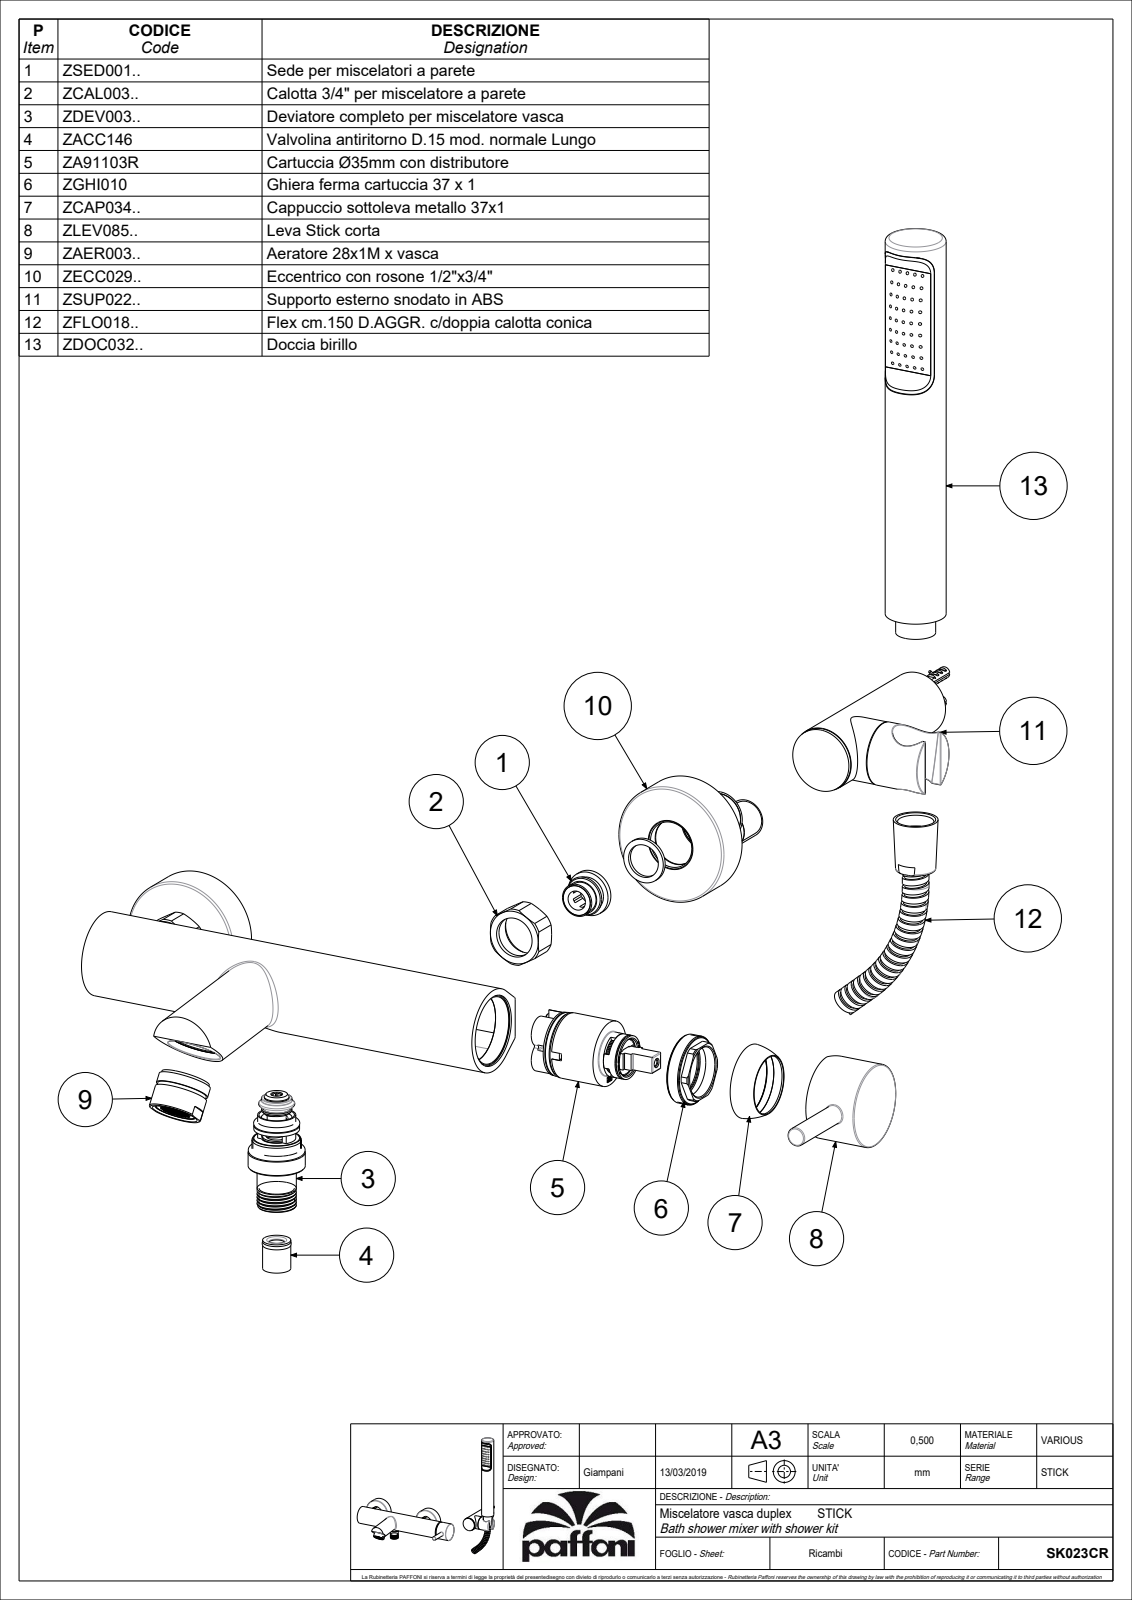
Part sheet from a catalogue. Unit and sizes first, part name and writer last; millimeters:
Units: millimetres
Overall size (bounding box): 424.5 × 381 × 152.4
Round holes (diameter × count): ⌀22 ×2, ⌀3 ×1, ⌀3.5 ×1, ⌀7.8 ×1, ⌀16 ×1, ⌀27.8 ×1, ⌀29 ×1, ⌀29.5 ×1, ⌀30.5 ×1, ⌀31 ×1, ⌀31.3 ×1
Round bosses / shafts (diameter × count): ⌀64.5 ×2, ⌀30 ×2, ⌀16 ×2, ⌀44.5 ×1, ⌀35.3 ×1, ⌀34.5 ×1, ⌀34 ×1, ⌀33.8 ×1
Partial cylindrical surfaces — rounded edges, fillets, slot ends (radius × count): R0.5 ×8, R0.3 ×6, R2 ×4, R5 ×4, R1.5 ×2, R15.5 ×2, R22.5 ×1
Main face-to-face distances: 20, 15.5, 35.5, 65, 2, 81, 29, 101, 65.5, 2.5
Hole centre spacings: 81.2, 150, 175.15, 231.2, 246.22, 388.1
Volume: 877 881 mm³ · Surface area: 153 310 mm²
Bodies: 3 solids, 469 faces (136 planar, 139 cylindrical, 194 other)
Part name (STEP PRODUCT): SK023CR
STEP written by: CREO PARAMETRIC BY PTC INC, 2020044 (CONFIG_CONTROL_DESIGN)
